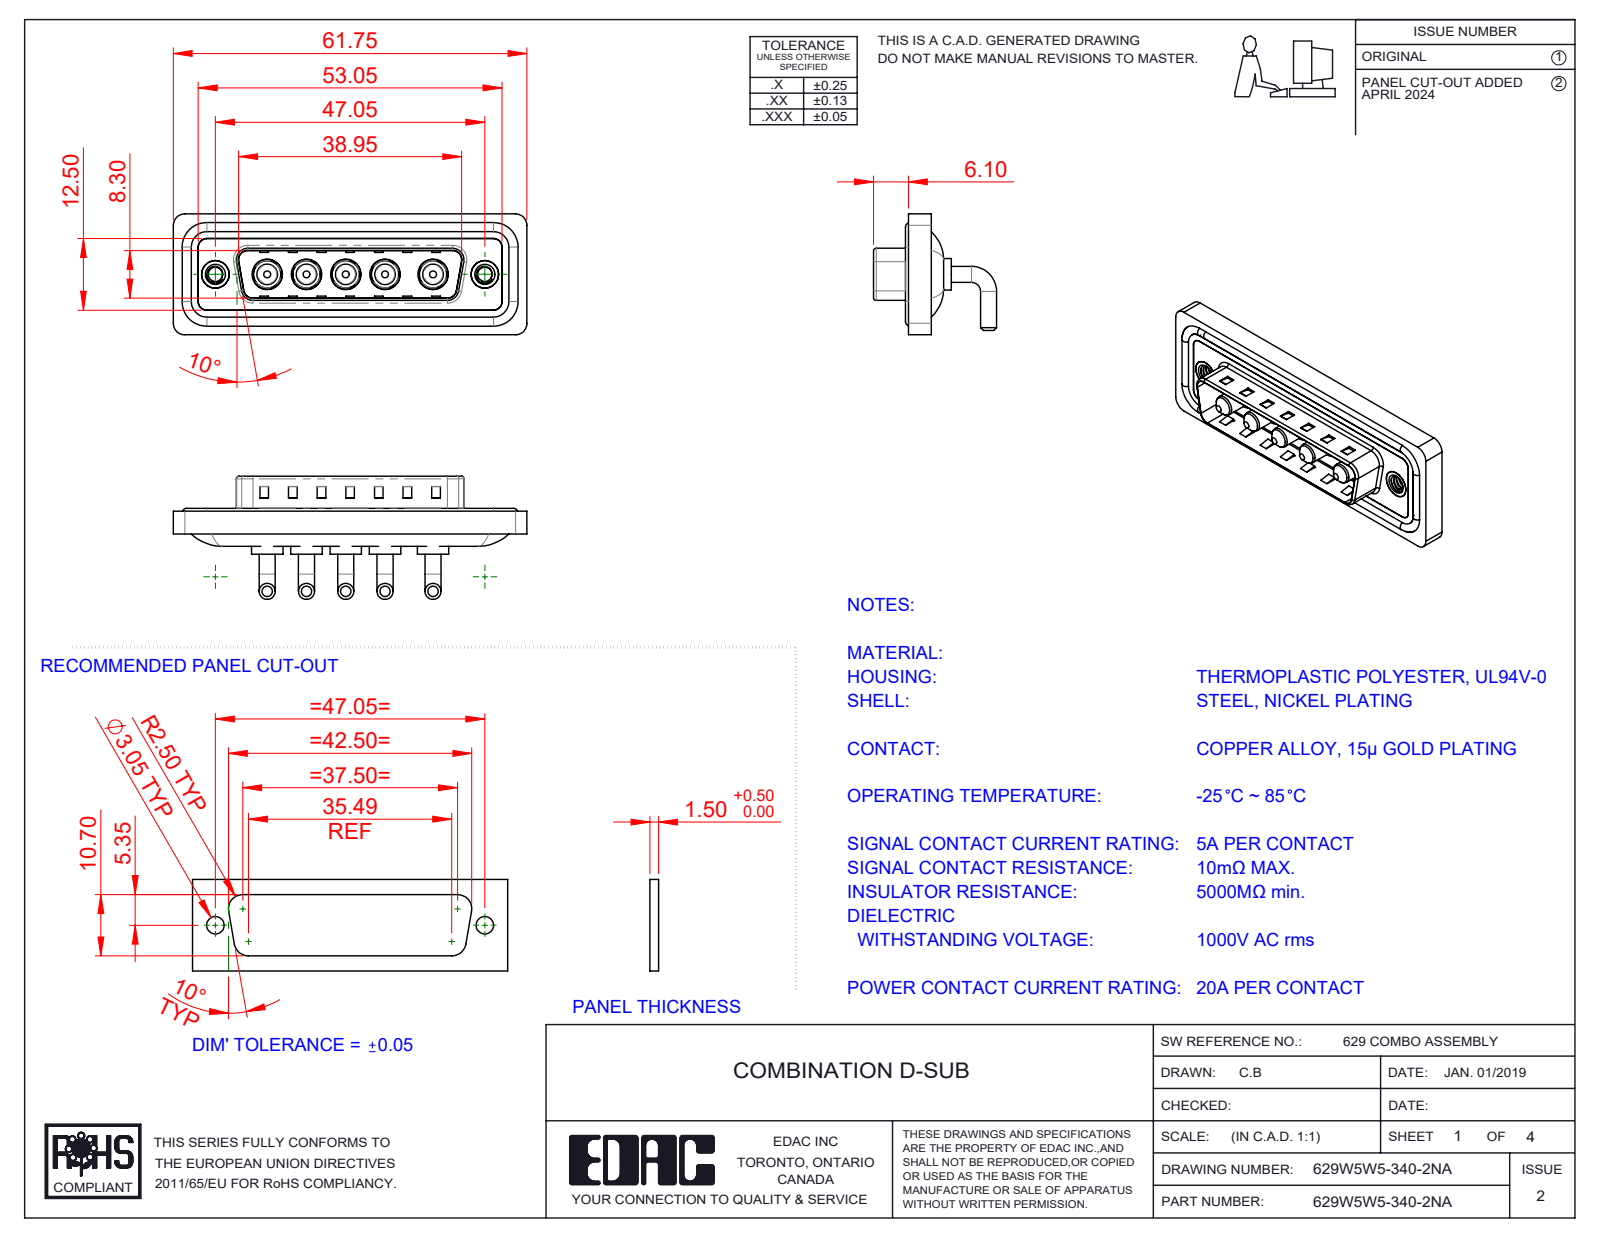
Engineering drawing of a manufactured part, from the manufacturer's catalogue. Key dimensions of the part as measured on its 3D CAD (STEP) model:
Part name (STEP PRODUCT): 629Combo Shell Rear_25 Contacts; 629Combo Waterproof Housing_25 Contacts; 629Combo Shell Front_25 Contacts; 629Combo Threaded Rivet_A (+3 more)
STEP written by: SolidWorks 2023 (CONFIG_CONTROL_DESIGN)
Units: millimetres
Bodies: 17 solids, 692 faces (259 planar, 291 cylindrical, 142 other)
Overall size (bounding box): 61.75 × 21.5 × 21.1
Volume: 7 805 mm³ · Surface area: 12 275 mm²
Round holes (diameter × count): ⌀4.85 ×5, ⌀5.3 ×5, ⌀2.5 ×2, ⌀4 ×2, ⌀4.8 ×2, ⌀5 ×2
Round bosses / shafts (diameter × count): ⌀2.8 ×10, ⌀5.5 ×5, ⌀5.2 ×5, ⌀4.75 ×5, ⌀3.75 ×5, ⌀3.6 ×5, ⌀1.6 ×4, ⌀4.9 ×2
Partial cylindrical surfaces — rounded edges, fillets, slot ends (radius × count): R1.5 ×18, R2 ×18, R0.5 ×8, R1.6 ×8, R2.1 ×5, R0.25 ×4, R0.6 ×4, R0.65 ×4
Main face-to-face distances: 0.4, 2.9, 0.8, 4.5, 4.1, 1.1, 2.1, 3.1, 1.5, 6
Hole centre spacings: 6.86, 13.73, 6.85, 6.87, 8.37, 8.38, 9.04, 9.05
